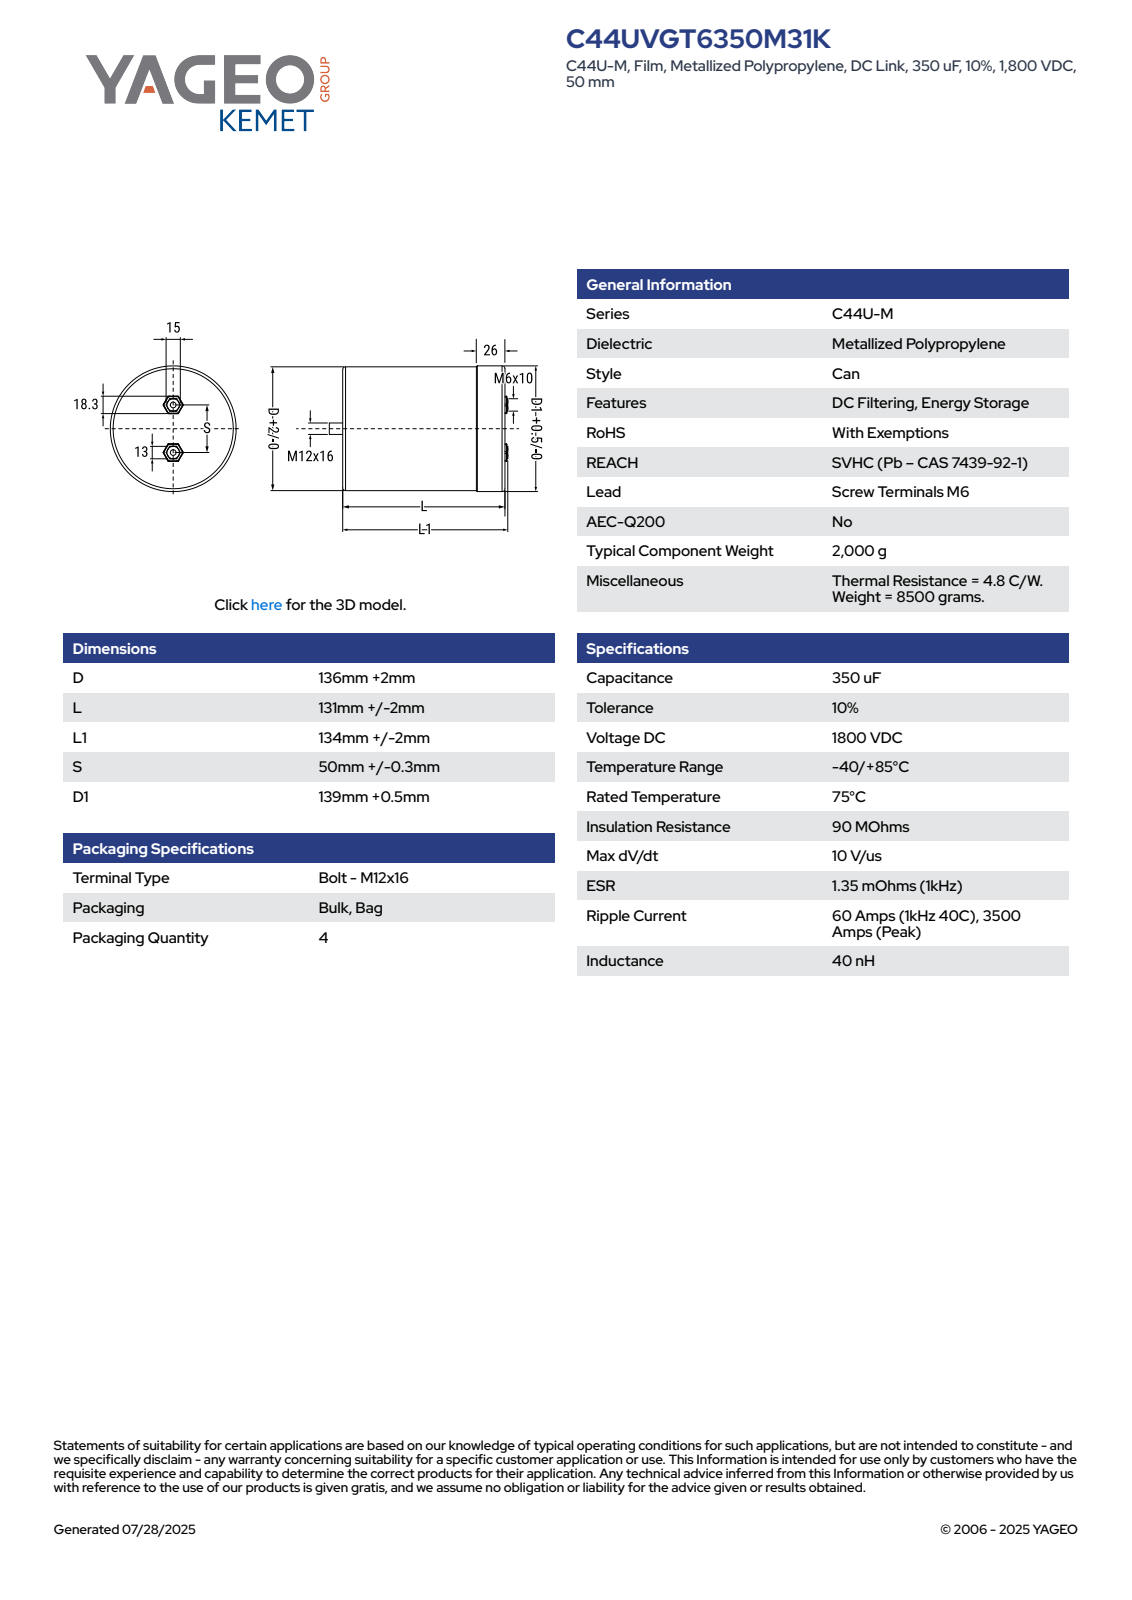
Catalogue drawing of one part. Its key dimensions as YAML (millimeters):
part_name: "CFP_C44UMH_136X131_D138L133S50L1136D1139.5"
step_written_by: "SolidWorks 2014 (AUTOMOTIVE_DESIGN)"
units: millimeters
bodies: {solids: 1, faces: 92, planar: 44, cylindrical: 17, other: 31}
overall_size: [152, 139.5, 139.5]
volume: 2000000
surface_area: 89673
round_holes:
  - {diameter: 6, count: 2}
round_bosses_or_shafts:
  - {diameter: 13, count: 2}
  - {diameter: 139.5, count: 1}
  - {diameter: 138, count: 1}
  - {diameter: 12, count: 1}
partial_cylinders:
  - {radius: 69.01, count: 1}
face_to_face_distances: [133, 107, 26, 135, 28, 2, 136, 29, 3, 1]
hole_center_spacings: [50]
